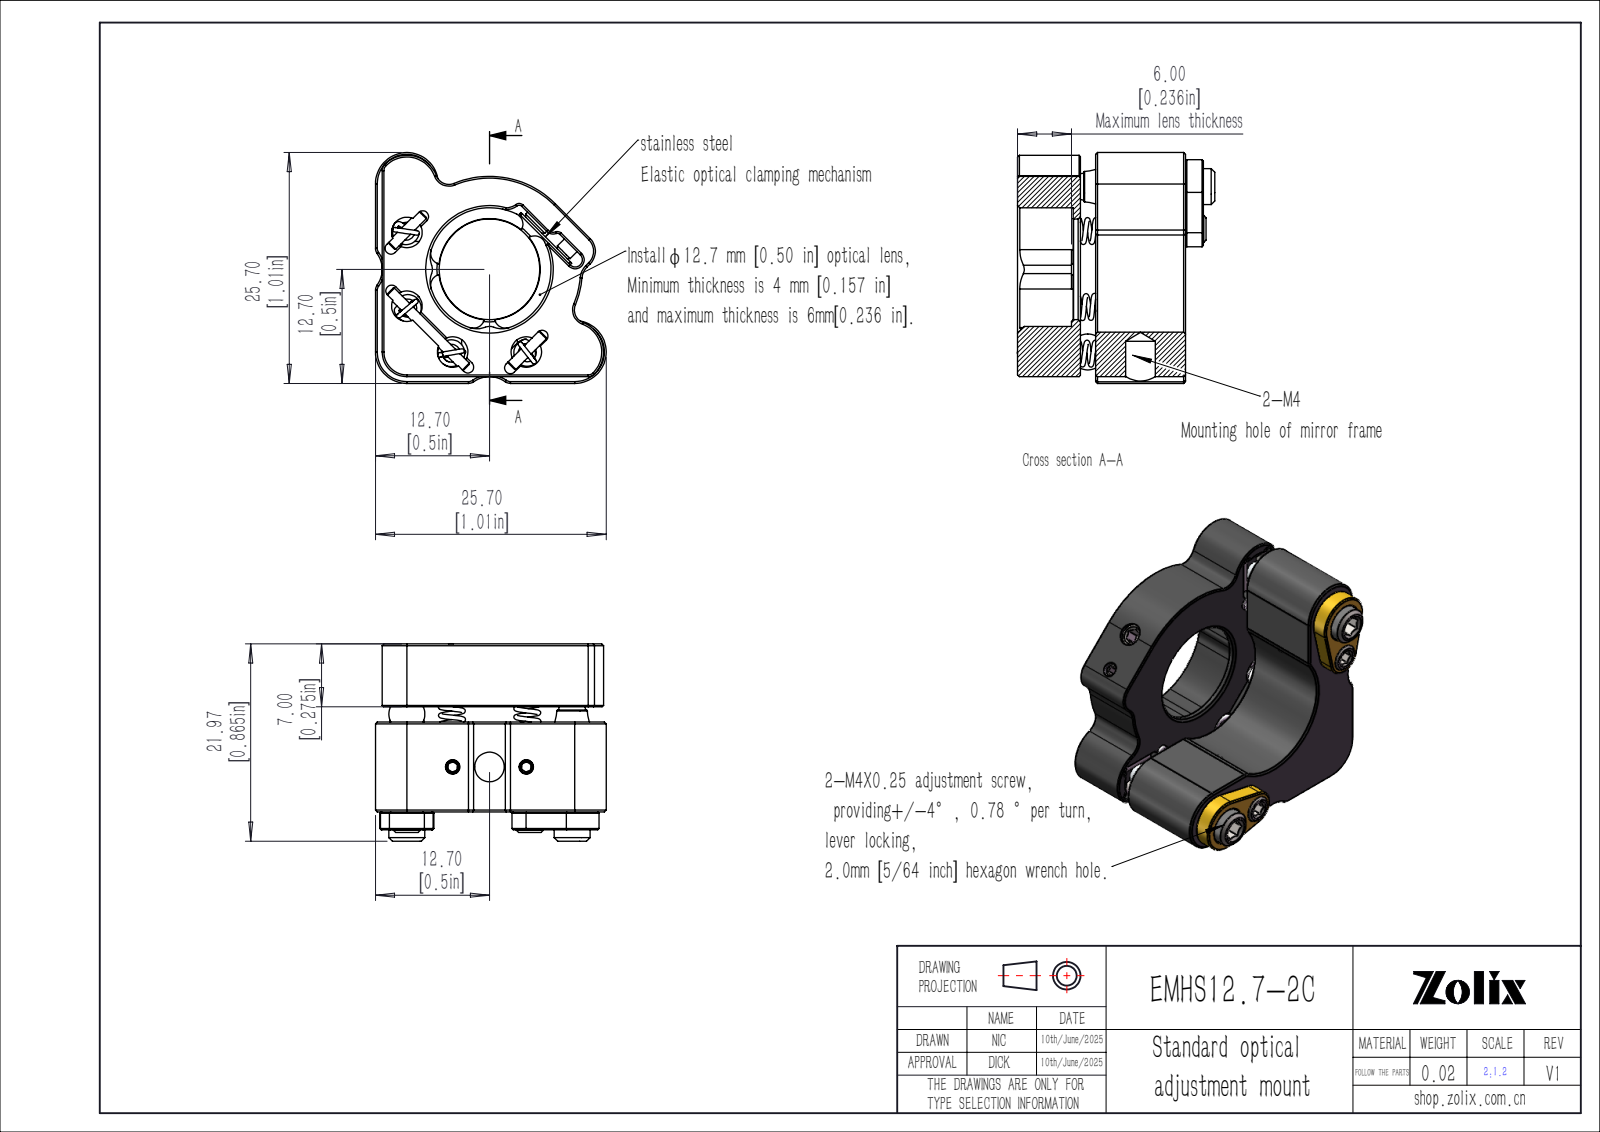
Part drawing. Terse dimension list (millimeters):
name: EMHS12.7-2C
written by: SolidWorks 2020 (CONFIG_CONTROL_DESIGN)
unit: mm
bodies: 29 solids, 742 faces (269 planar, 194 cylindrical, 279 other)
size: 25.7 × 25.7 × 22
volume: 4 942 mm³; area: 6 193 mm²
holes: 5× ⌀1.6, 4× ⌀3.4, 4× ⌀3.5, 3× ⌀2.5, 2× ⌀2.99, 2× ⌀3.2, 2× ⌀3.3, 2× ⌀3.75, 2× ⌀4, 1× ⌀11.2
bosses: 7× ⌀1.2, 5× ⌀2, 3× ⌀3
rounds: 14× R0.65, 9× R1, 8× R1.25, 5× R0.2, 5× R2, 5× R3.5, 4× R1.5, 4× R2.5
face distances: 7, 11.7, 0.75, 18.7, 10, 1.7, 8.7, 6.25, 0.8, 3.2
hole spacings: 4.1, 8.2, 10.07, 19.09, 0.4, 4.7, 5.1, 8.6
